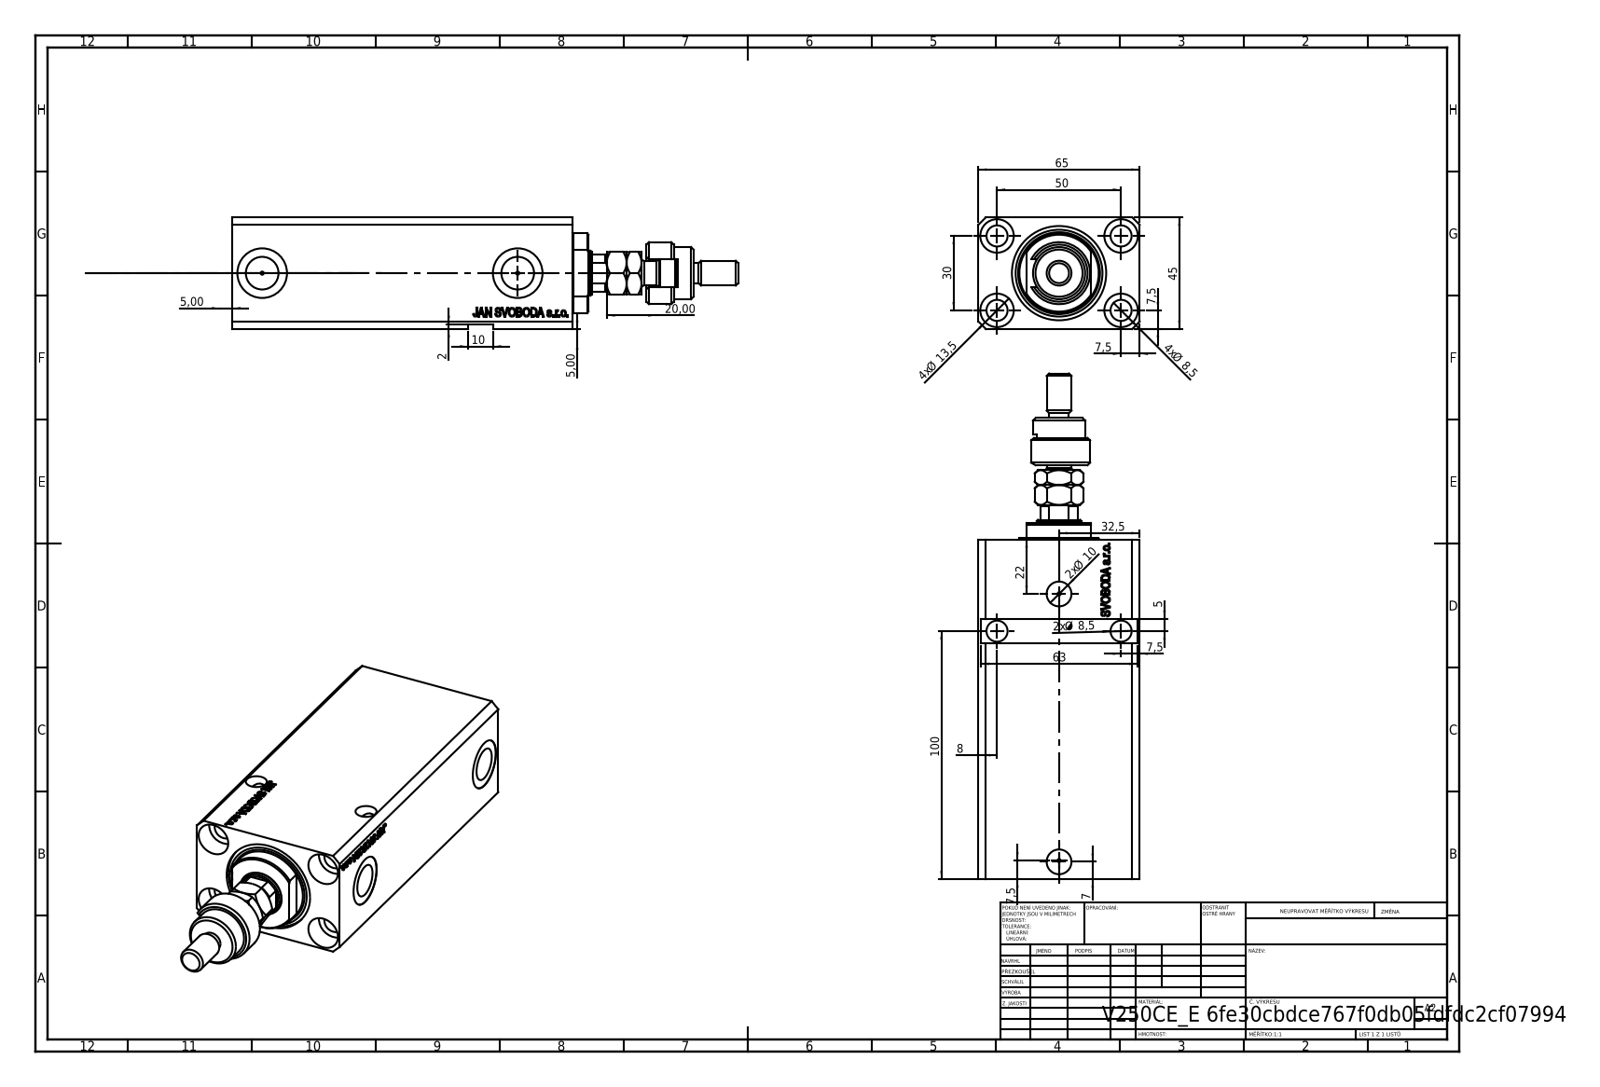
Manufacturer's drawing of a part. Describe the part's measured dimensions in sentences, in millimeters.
The part is named "FEMALE_PART_FOR_DFA; V250CE_VC_E; V250CE_C_VCP; V250CE_E_Body (+1 more)". Its 3-D file was written by "SolidWorks 2019 (CONFIG_CONTROL_DESIGN)". It is 5 solids with 998 faces: 467 planar, 109 cylindrical and 422 other. Overall it measures 203.9 by 65 by 45 millimeters. Its volume is 346 508 cubic millimeters and its surface area 88 213 square millimeters. Round holes: 7 of diameter 8.5, 4 of diameter 1.25, 4 of diameter 13.5, 2 of diameter 10, 2 of diameter 13.16, 2 of diameter 20, 1 of diameter 18, 1 of diameter 38. Round bosses or shafts: 1 of diameter 25, 1 of diameter 21, 1 of diameter 16, 1 of diameter 10, 1 of diameter 8. Partial cylindrical surfaces (rounded edges, fillets, slot ends): 1 of radius 5.5, 1 of radius 8.5, 1 of radius 8.75, 1 of radius 16. The main face-to-face distances are 45, 65, 111.9, 137, 25.1, 6.9, 105, 130.1, 13, 14. The hole center spacings are 29.15, 50, 30, 58.31, 95.79, 96.3, 0.53, 103.
